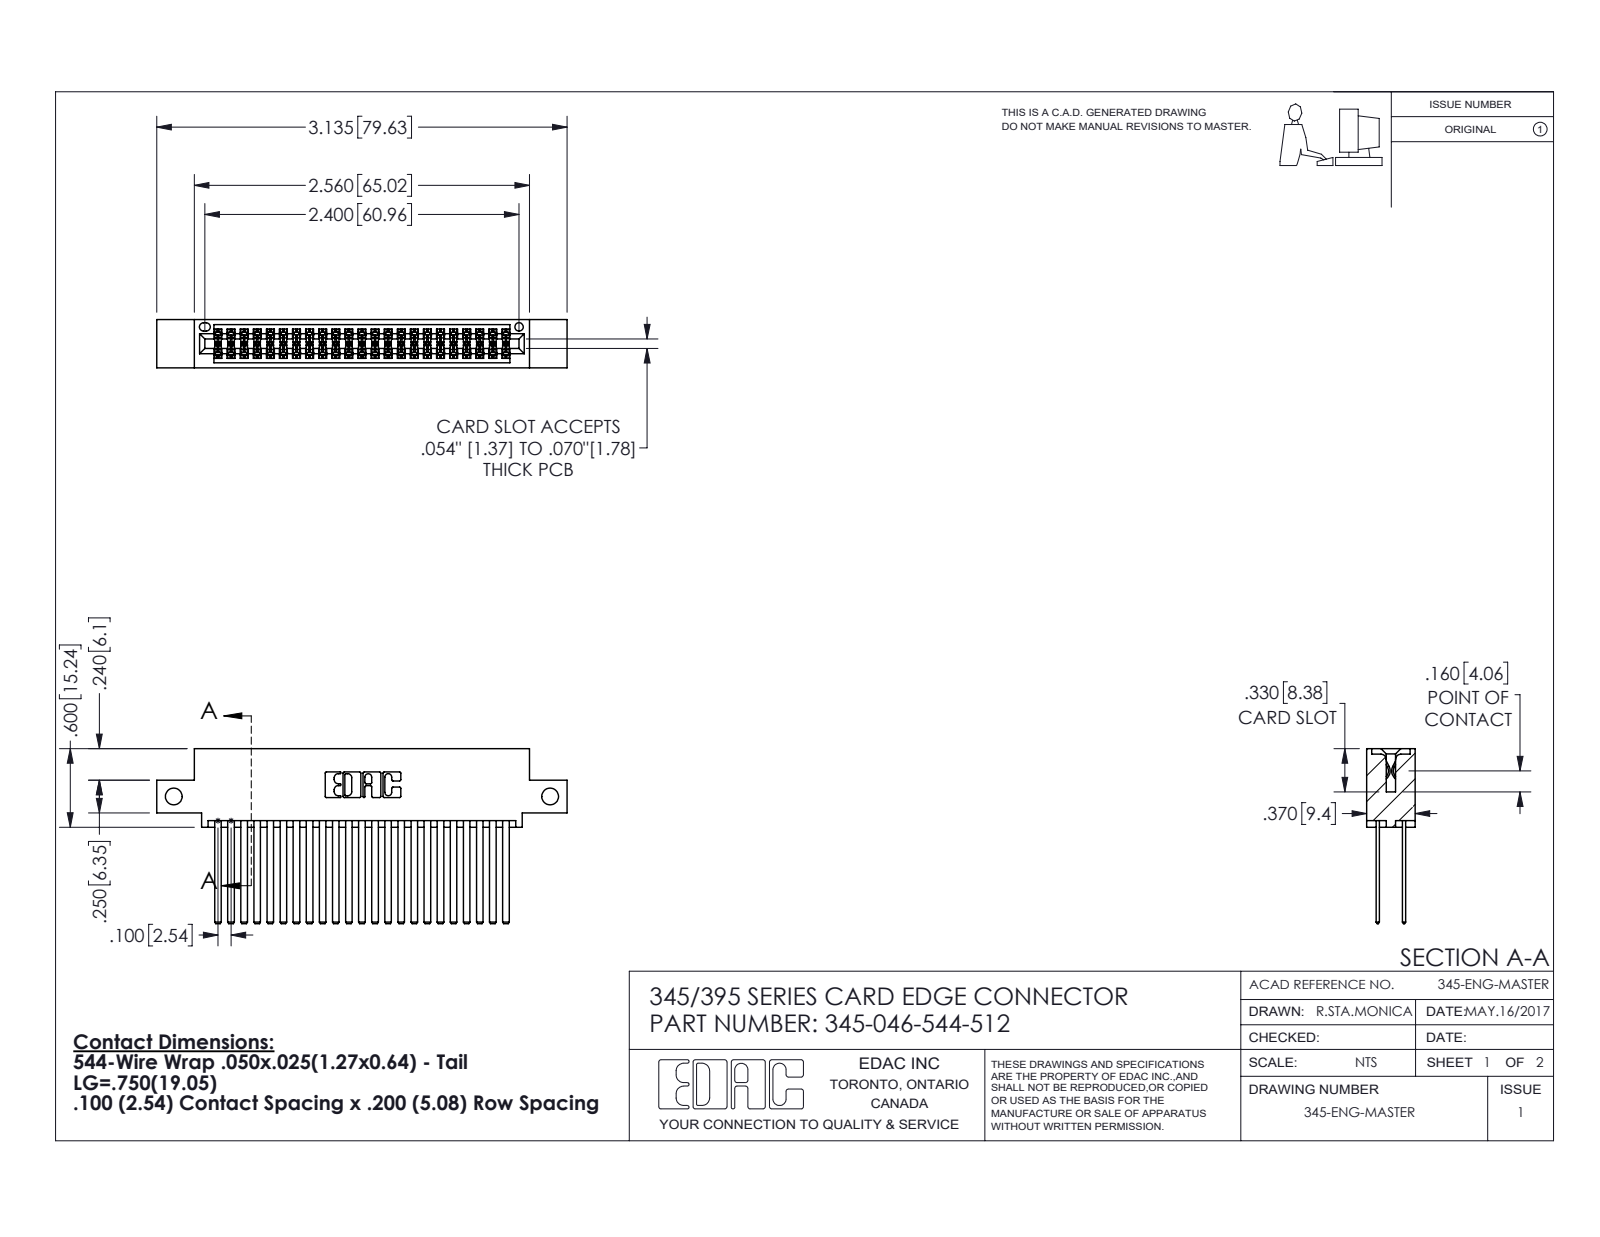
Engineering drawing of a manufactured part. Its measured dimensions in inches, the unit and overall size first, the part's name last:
Units: inches
Overall size (bounding box): 3.135 × 1.337 × 0.37
Round holes (diameter × count): ⌀0.128 ×2, ⌀0.064 ×1
Partial cylindrical surfaces — rounded edges, fillets, slot ends (radius × count): R0.006 ×69, R0.01 ×22, R0.007 ×6, R0.031 ×6, R0.026 ×3, R0.014 ×2, R0.019 ×2, R0.022 ×2
Main face-to-face distances: 0.2, 0.298, 0.072, 0.025, 0.098, 0.272, 0.225, 0.175, 0.37, 0.05
Hole centre spacings: 2.875
Volume: 0.491 in³ · Surface area: 20.72 in²
Bodies: 47 solids, 2154 faces (1418 planar, 736 cylindrical, 0 other)
Part name (STEP PRODUCT): 345-292-001_345-293-144; 345 Part_0.110 Offset - Side Mount; 345-046-544-512
STEP written by: SolidWorks 2016 (CONFIG_CONTROL_DESIGN)
